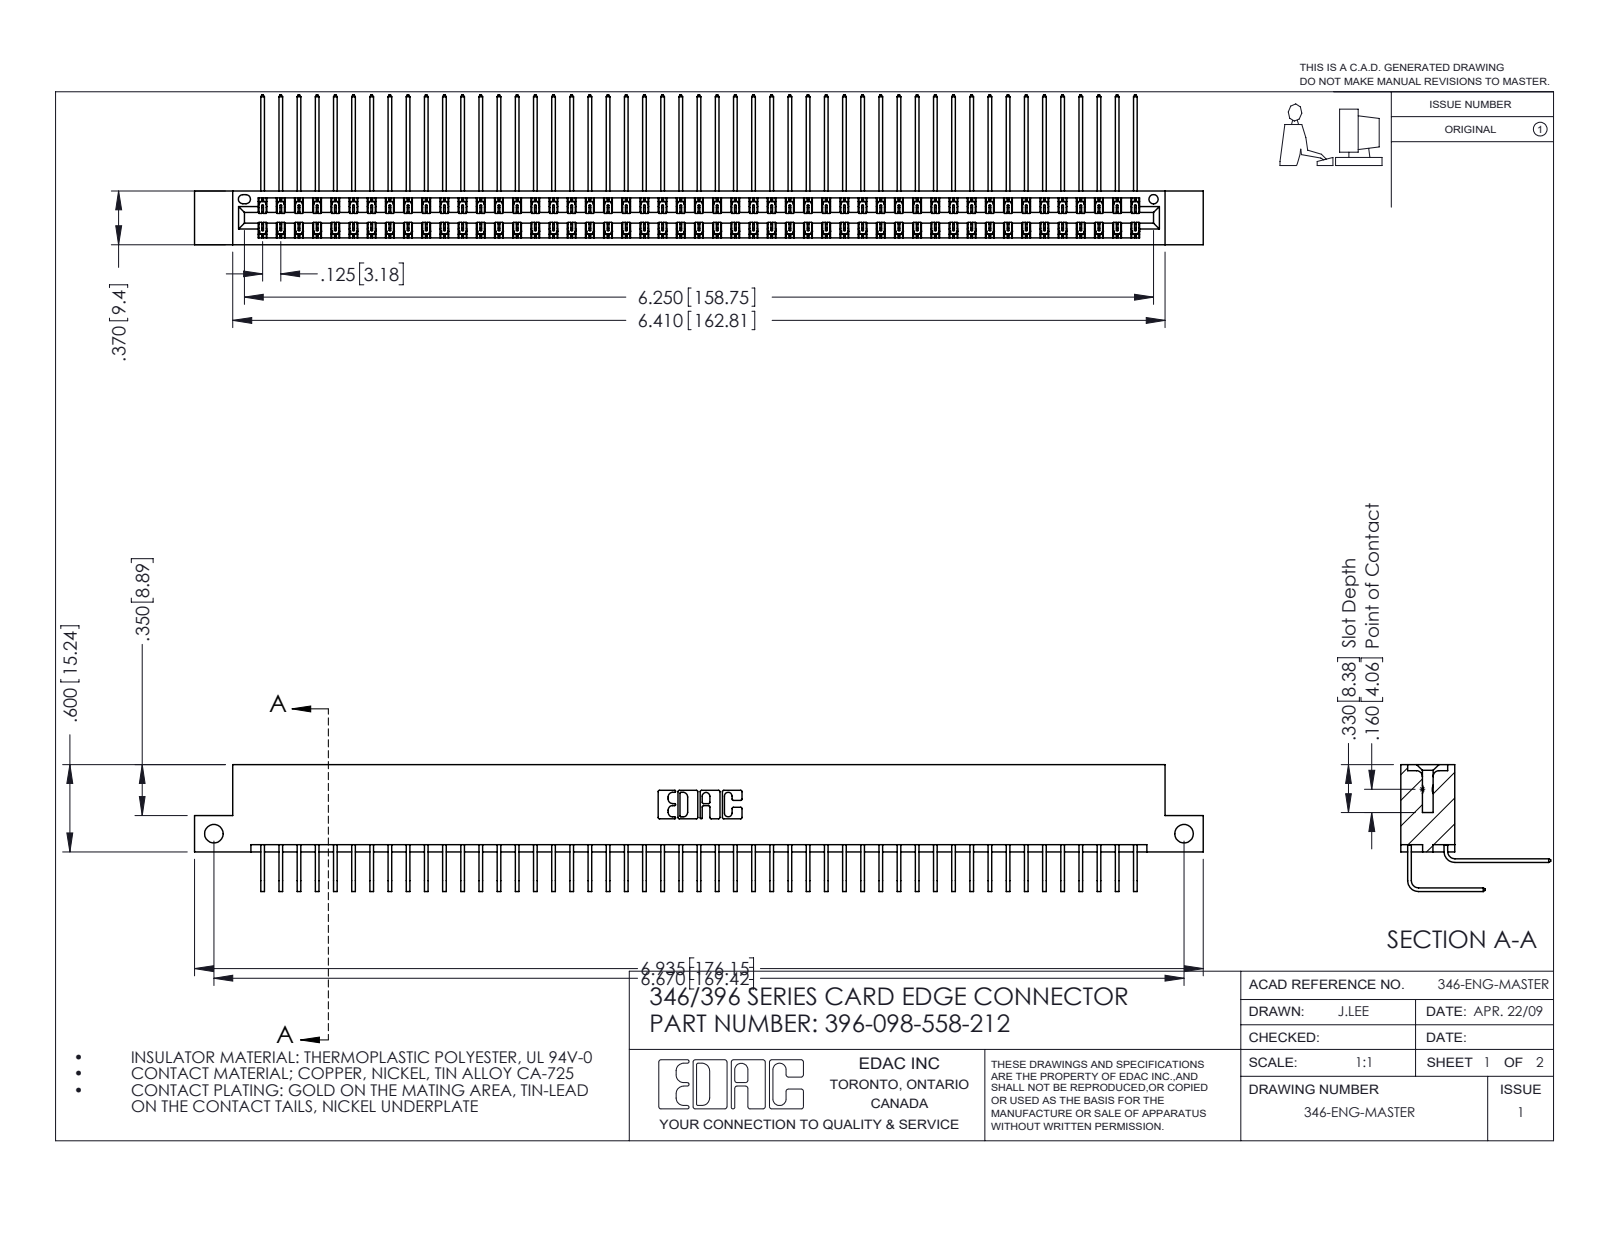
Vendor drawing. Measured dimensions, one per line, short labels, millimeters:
name: 345-292-001_558 Tail - 2; 346 Part_Flush Mounting Lugs - Side Mount; 396-098-558-212; 345-292-001_558 559 Tail - 1
written by: SolidWorks 2016 (CONFIG_CONTROL_DESIGN)
unit: mm
bodies: 99 solids, 5414 faces (3702 planar, 1712 cylindrical, 0 other)
size: 176.1 × 26.2 × 22.2
volume: 17 710 mm³; area: 27 030 mm²
holes: 2× ⌀3.3, 1× ⌀1.6
rounds: 147× R0.2, 22× R0.3, 6× R0.2, 6× R0.8, 3× R0.7, 2× R0.4, 2× R0.6, 2× R0.6
face distances: 8.2, 1.2, 0.6, 9.4, 6.4, 7.6, 1.8, 7, 3.8, 5.6
hole spacings: 169.4
